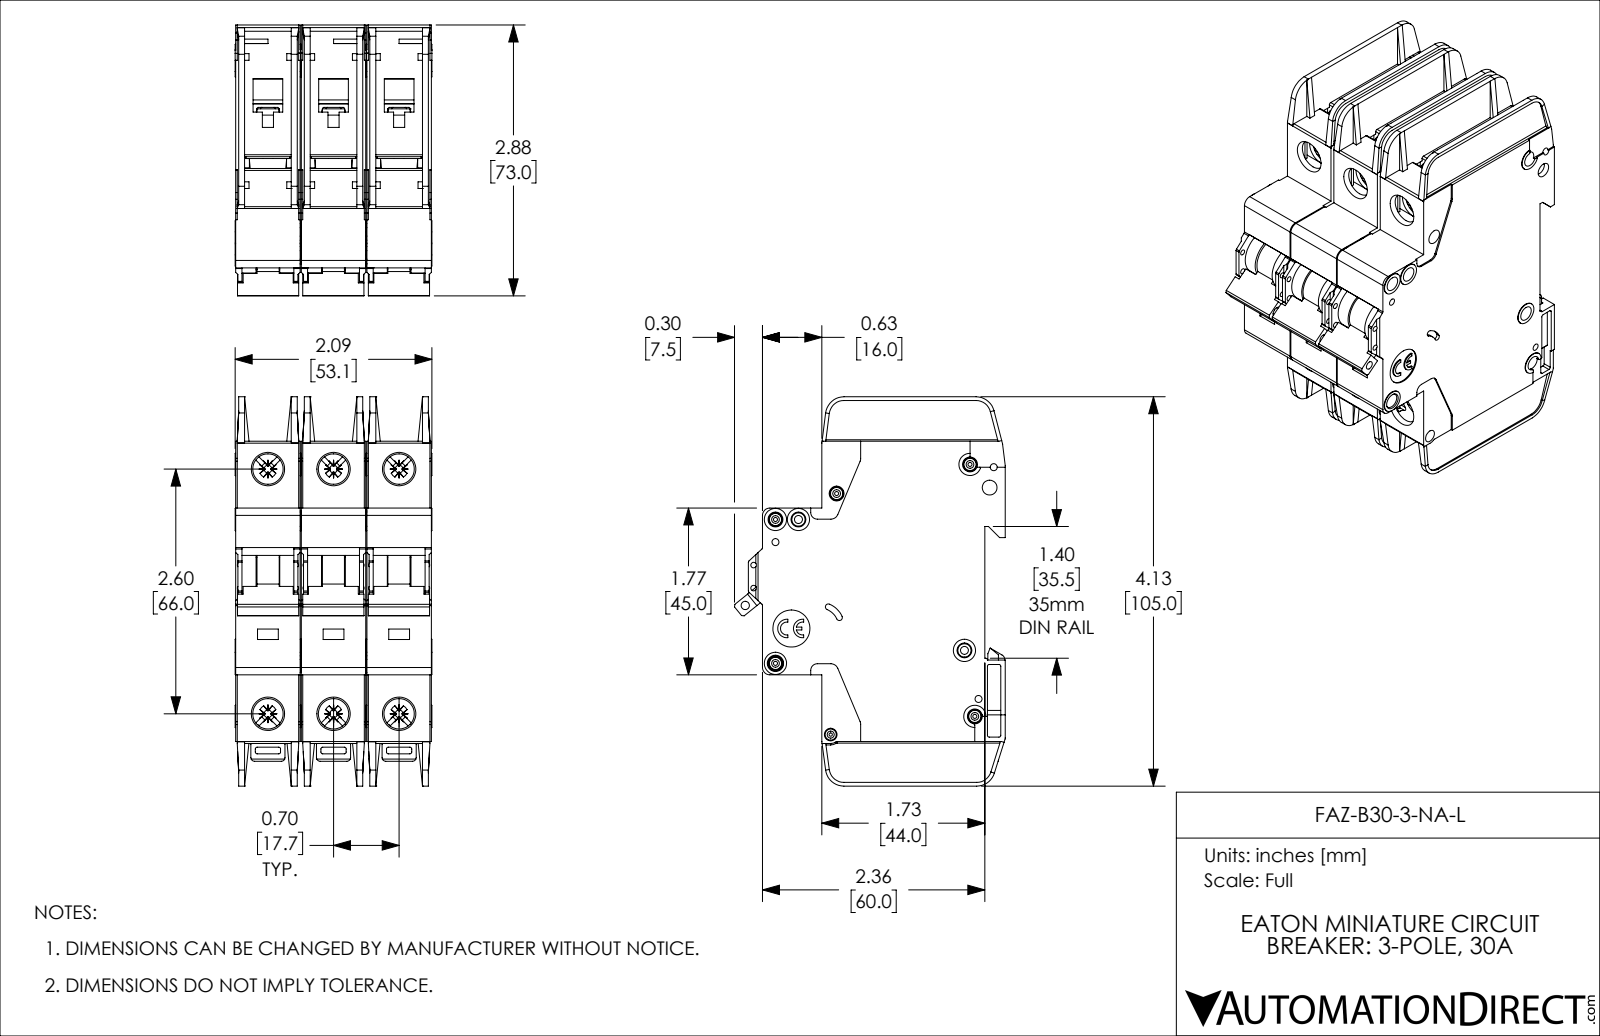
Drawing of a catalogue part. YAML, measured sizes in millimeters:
part_name: "FAZ-B30-3-NA-L"
step_written_by: "SolidWorks 2019 (AUTOMOTIVE_DESIGN)"
units: millimeters
bodies: {solids: 3, faces: 3381, planar: 2013, cylindrical: 1071, other: 297}
overall_size: [105, 73.1, 53.1]
volume: 230200
surface_area: 79350
round_holes:
  - {diameter: 4, count: 8}
  - {diameter: 8.2, count: 6}
  - {diameter: 1.1, count: 5}
  - {diameter: 1.9, count: 4}
  - {diameter: 1.5, count: 2}
  - {diameter: 2.2, count: 2}
  - {diameter: 0.9, count: 1}
  - {diameter: 2.3, count: 1}
  - {diameter: 2.5, count: 1}
  - {diameter: 3.4, count: 1}
  - {diameter: 10, count: 1}
round_bosses_or_shafts:
  - {diameter: 3.3, count: 5}
  - {diameter: 6, count: 4}
  - {diameter: 3, count: 4}
  - {diameter: 2.5, count: 3}
partial_cylinders:
  - {radius: 0.5, count: 72}
  - {radius: 0.4, count: 30}
  - {radius: 1, count: 18}
  - {radius: 1.1, count: 12}
  - {radius: 2, count: 12}
  - {radius: 0.2, count: 6}
  - {radius: 0.3, count: 6}
  - {radius: 0.7, count: 6}
face_to_face_distances: [17.7, 1.2, 35.4, 17.4, 15, 35.1, 18.9, 16.5, 2.7, 2.4]
hole_center_spacings: [17.7, 68.3, 66, 6.2, 13.6, 22.1, 35.4, 74.9]
